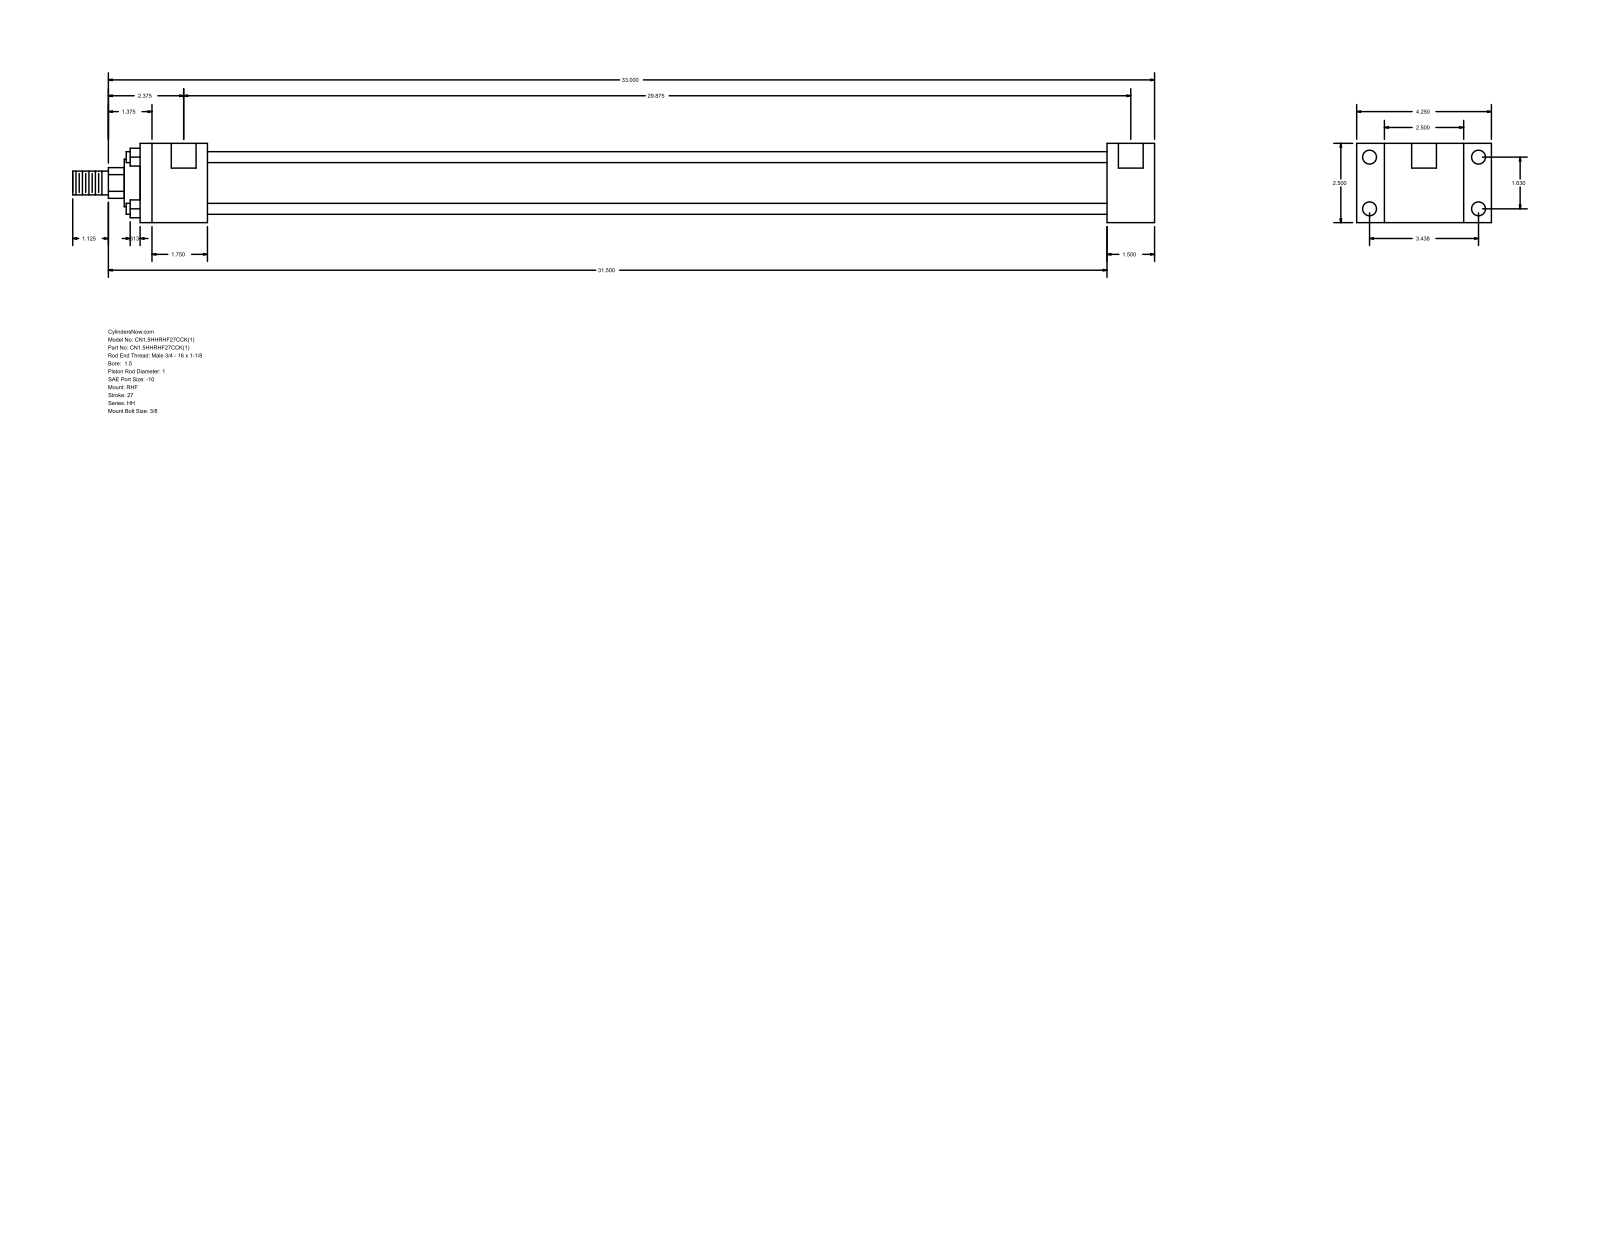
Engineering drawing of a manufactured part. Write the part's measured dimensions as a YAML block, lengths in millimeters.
part_name: "HH_RHF__0150_1"
step_written_by: "GSSL Pune (CONFIG_CONTROL_DESIGN)"
units: millimeters
bodies: {solids: 0, faces: 88, planar: 60, cylindrical: 28, other: 0}
overall_size: [866.77, 107.95, 63.5]
round_holes:
  - {diameter: 5.56, count: 4}
  - {diameter: 11.13, count: 4}
  - {diameter: 19.84, count: 2}
round_bosses_or_shafts:
  - {diameter: 8.76, count: 4}
  - {diameter: 44.45, count: 1}
  - {diameter: 38.1, count: 1}
  - {diameter: 25.4, count: 1}
  - {diameter: 19.05, count: 1}
partial_cylinders:
  - {radius: 12.29, count: 1}
face_to_face_distances: [63.5, 22.23, 85.73, 38.1, 107.96, 720.72, 758.82, 53.98, 774.7, 812.8]
hole_center_spacings: [1.59, 41.4, 87.32, 96.64, 760.41, 762, 758.82]
